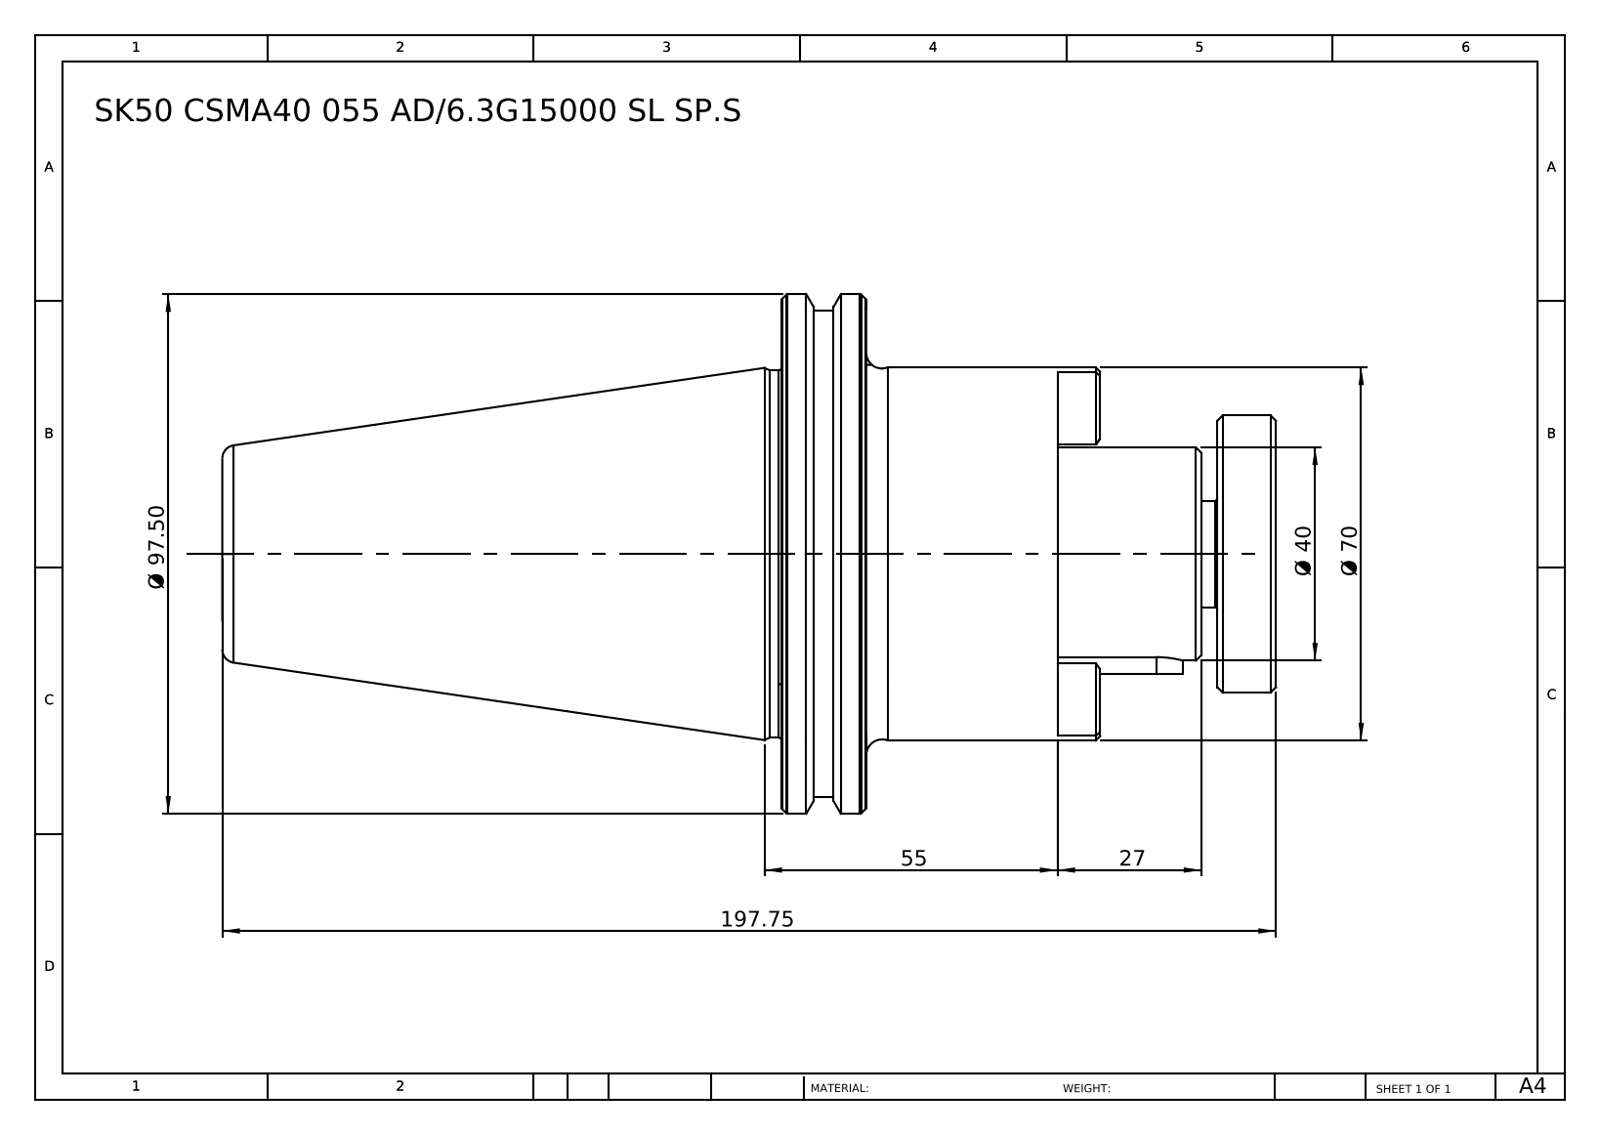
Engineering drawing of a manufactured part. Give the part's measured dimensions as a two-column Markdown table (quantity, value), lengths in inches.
| quantity | value |
| --- | --- |
| part name | SK 50 CSMA40 055 AD-6.3G15000 SL SP |
| STEP written by | SolidWorks 2014 (CONFIG_CONTROL_DESIGN) |
| units | inches |
| bodies | 1 solid, 116 faces (22 planar, 20 cylindrical, 74 other) |
| overall size | 7.785 × 3.839 × 3.839 |
| volume | 35.02 in³ |
| surface area | 83.22 in² |
| round bosses / shafts (diameter × count) | 3.839 × 1, 3.593 × 1, 2.756 × 1, 2.717 × 1, 2.047 × 1, 1.575 × 1, 0.787 × 1 |
| partial cylindrical surfaces (radius × count) | 0.197 × 1, 0.866 × 1 |
| main face-to-face distances | 0.626, 1.413, 2.039, 1.614, 3.028, 3.654, 0.433, 1.181, 2.594, 3.22 |
